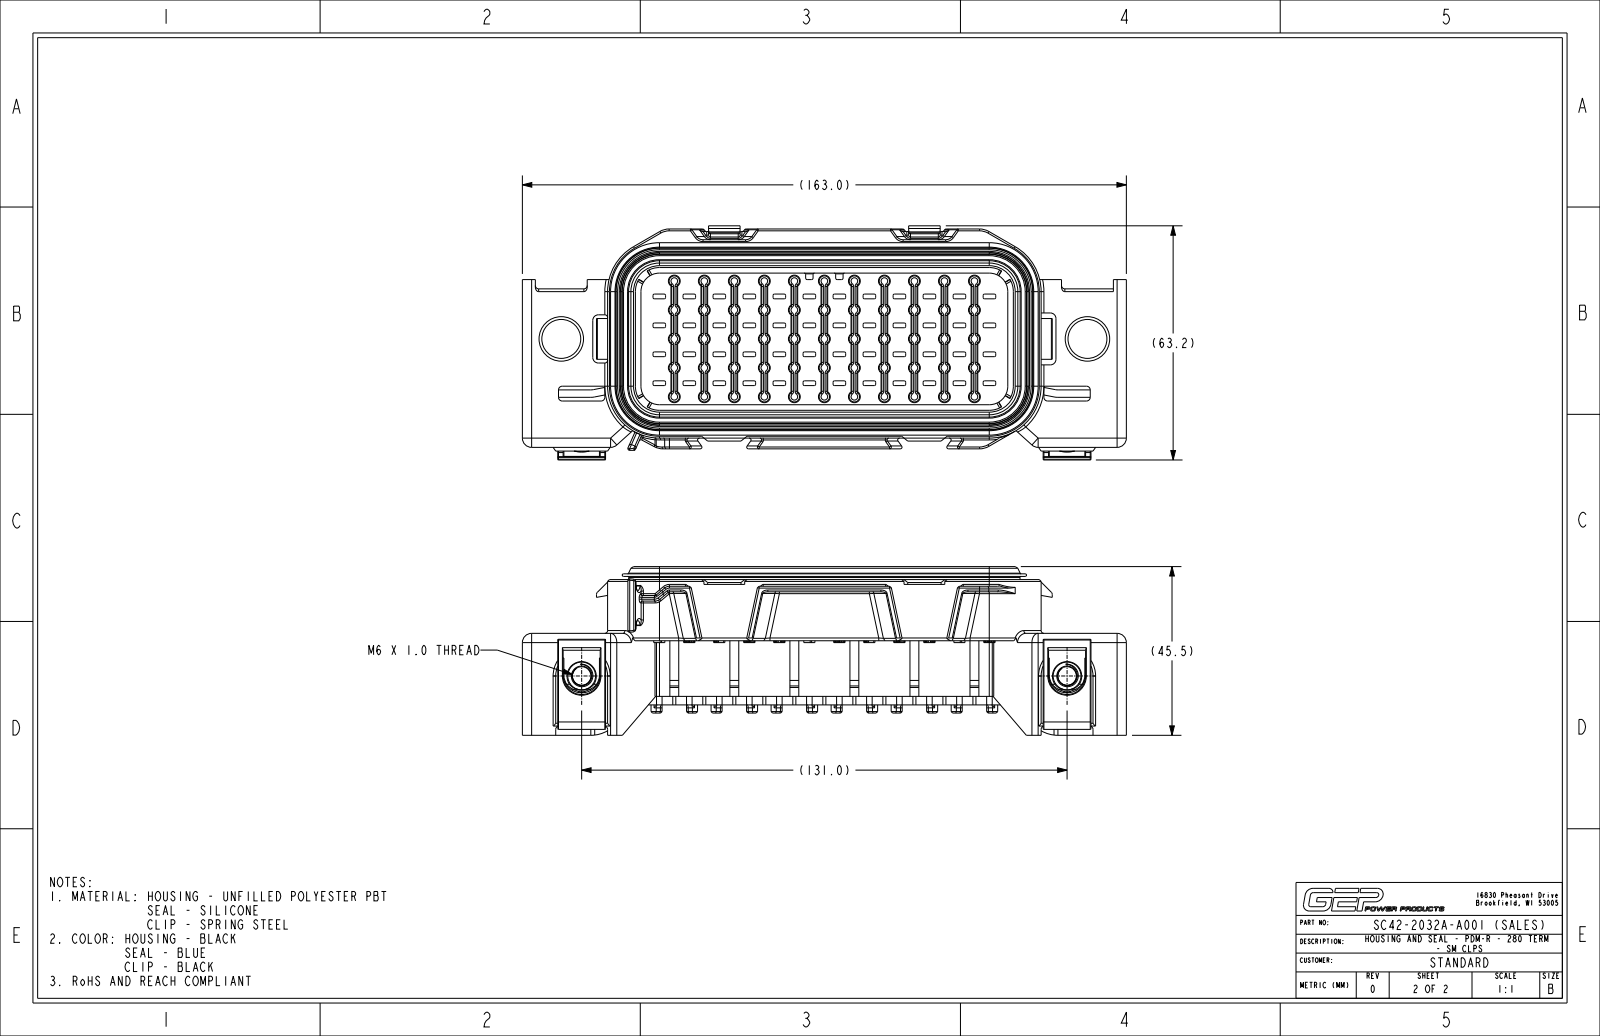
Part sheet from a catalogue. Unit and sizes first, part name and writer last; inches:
Units: inches
Overall size (bounding box): 6.417 × 2.487 × 1.791
Round holes (diameter × count): ⌀0.264 ×48, ⌀0.413 ×4, ⌀0.197 ×2, ⌀0.295 ×2, ⌀0.492 ×2
Round bosses / shafts (diameter × count): ⌀0.276 ×2, ⌀0.197 ×1, ⌀0.098 ×1
Partial cylindrical surfaces — rounded edges, fillets, slot ends (radius × count): R0.02 ×545, R0.016 ×205, R0.008 ×68, R0.031 ×62, R0.055 ×55, R0.175 ×48, R0.012 ×46, R0.035 ×39
Main face-to-face distances: 0.079, 0.276, 0.059, 0.217, 0.071, 0.453, 0.354, 0.098, 0.295, 1.673
Hole centre spacings: 0.443, 0.319, 0.692, 0.708, 0.307, 2.57, 0.638, 2.253
Volume: 7.555 in³ · Surface area: 143.9 in²
Bodies: 1 solid, 6650 faces (2830 planar, 1780 cylindrical, 2040 other)
Part name (STEP PRODUCT): SC42-2032A-A001_NCF_SW0001
STEP written by: CREO PARAMETRIC BY PTC INC, 2024014 (CONFIG_CONTROL_DESIGN)
